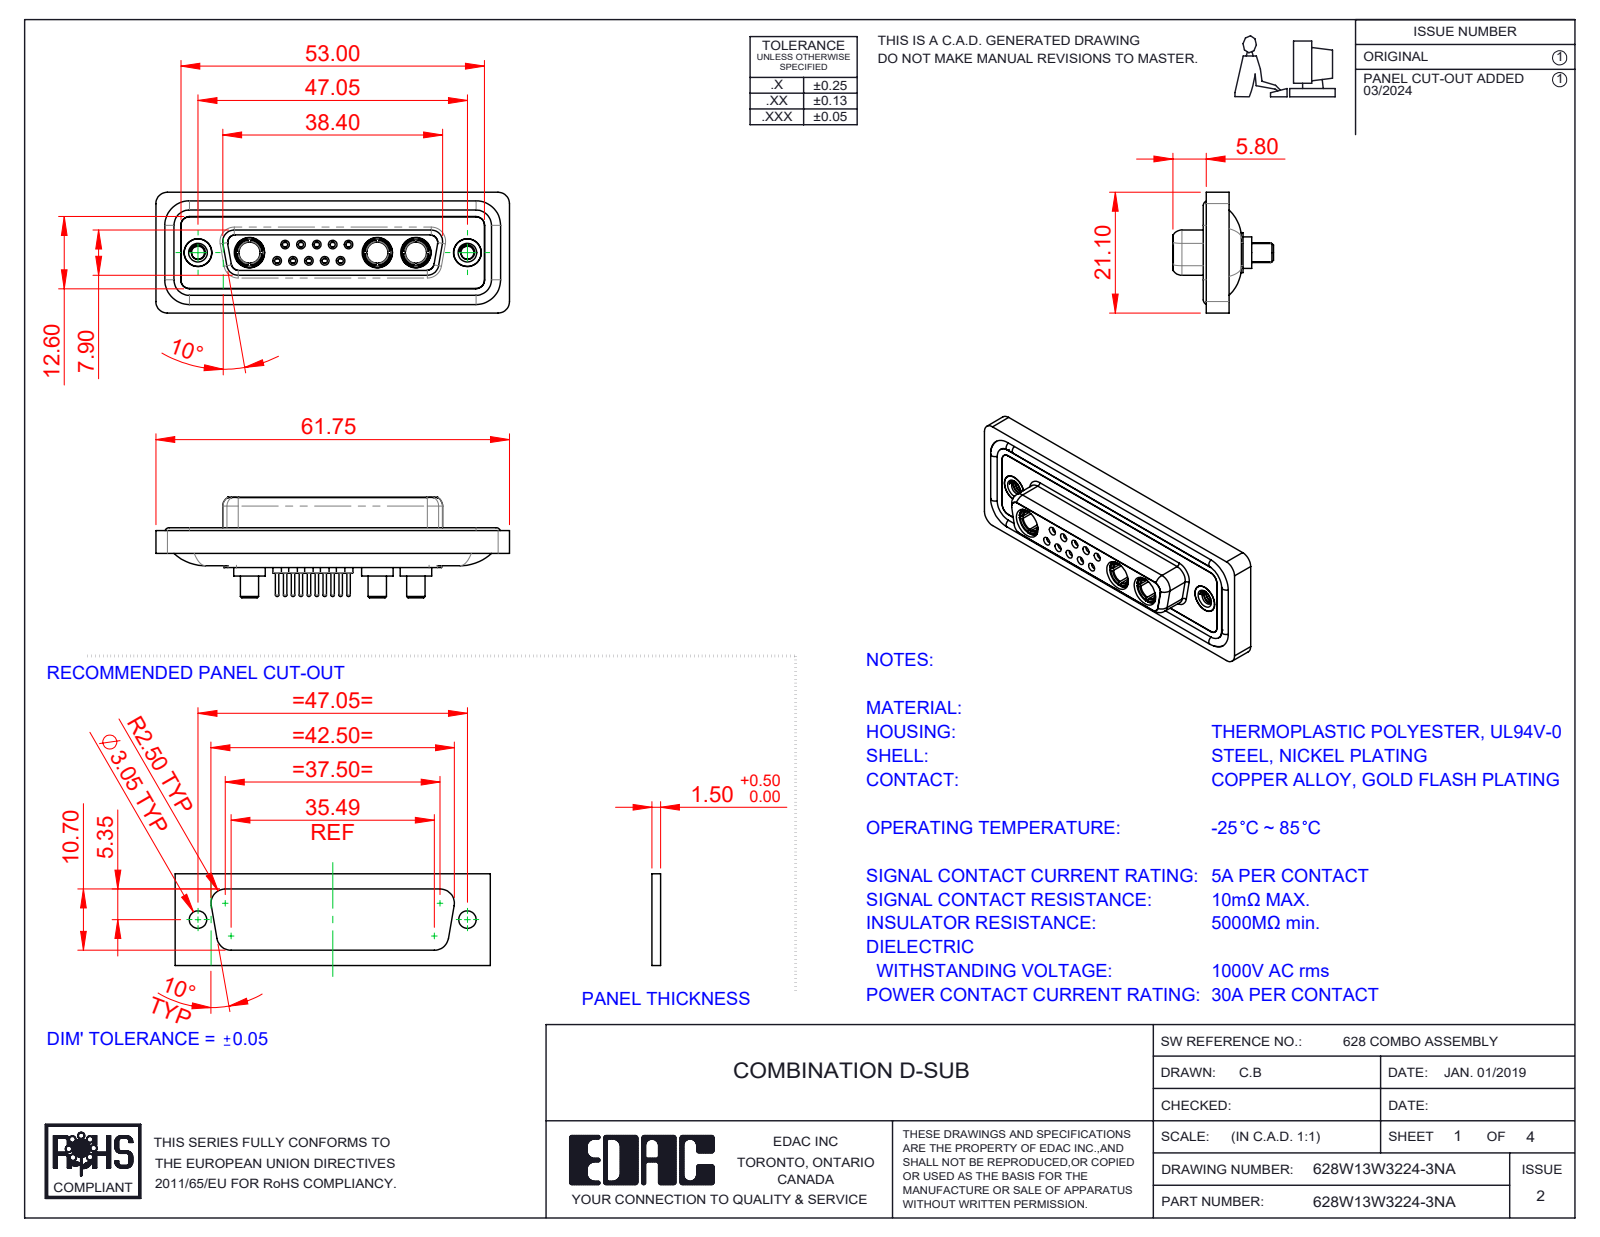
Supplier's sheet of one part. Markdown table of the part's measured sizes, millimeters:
| quantity | value |
| --- | --- |
| part name | 628Combo Contact Row 1_24; Power Socket_30A S; 628Combo Threaded Rivet_A; 628Combo Contact Row 2_24 (+5 more) |
| STEP written by | SolidWorks 2023 (CONFIG_CONTROL_DESIGN) |
| units | millimeters |
| bodies | 23 solids, 1156 faces (342 planar, 449 cylindrical, 365 other) |
| overall size | 61.75 × 21.1 × 17.55 |
| volume | 8 296 mm³ |
| surface area | 13 720 mm² |
| round holes (diameter × count) | 0.9 × 10, 1.1 × 10, 1.5 × 10, 2 × 10, 1.6 × 5, 1.7 × 5, 4.85 × 5, 3.7 × 3, 5.3 × 3, 2.26 × 2, 4 × 2, 4.05 × 2 |
| round bosses / shafts (diameter × count) | 2.2 × 10, 0.6 × 10, 1.6 × 9, 5.5 × 3, 5.2 × 3, 4.96 × 3, 4.75 × 3, 3.75 × 3 |
| partial cylindrical surfaces (radius × count) | 1.5 × 22, 2 × 18, 1.35 × 8, 1.6 × 8, 0.25 × 4, 0.5 × 4, 0.6 × 4, 0.65 × 4 |
| main face-to-face distances | 0.4, 1.8, 7.45, 5.65, 0.5, 6.6, 7.05, 1.6, 2.9, 1.1 |
| hole center spacings | 3.16, 2.77, 5.03, 5.04, 5.54, 8.31, 7.49, 2.76 |
